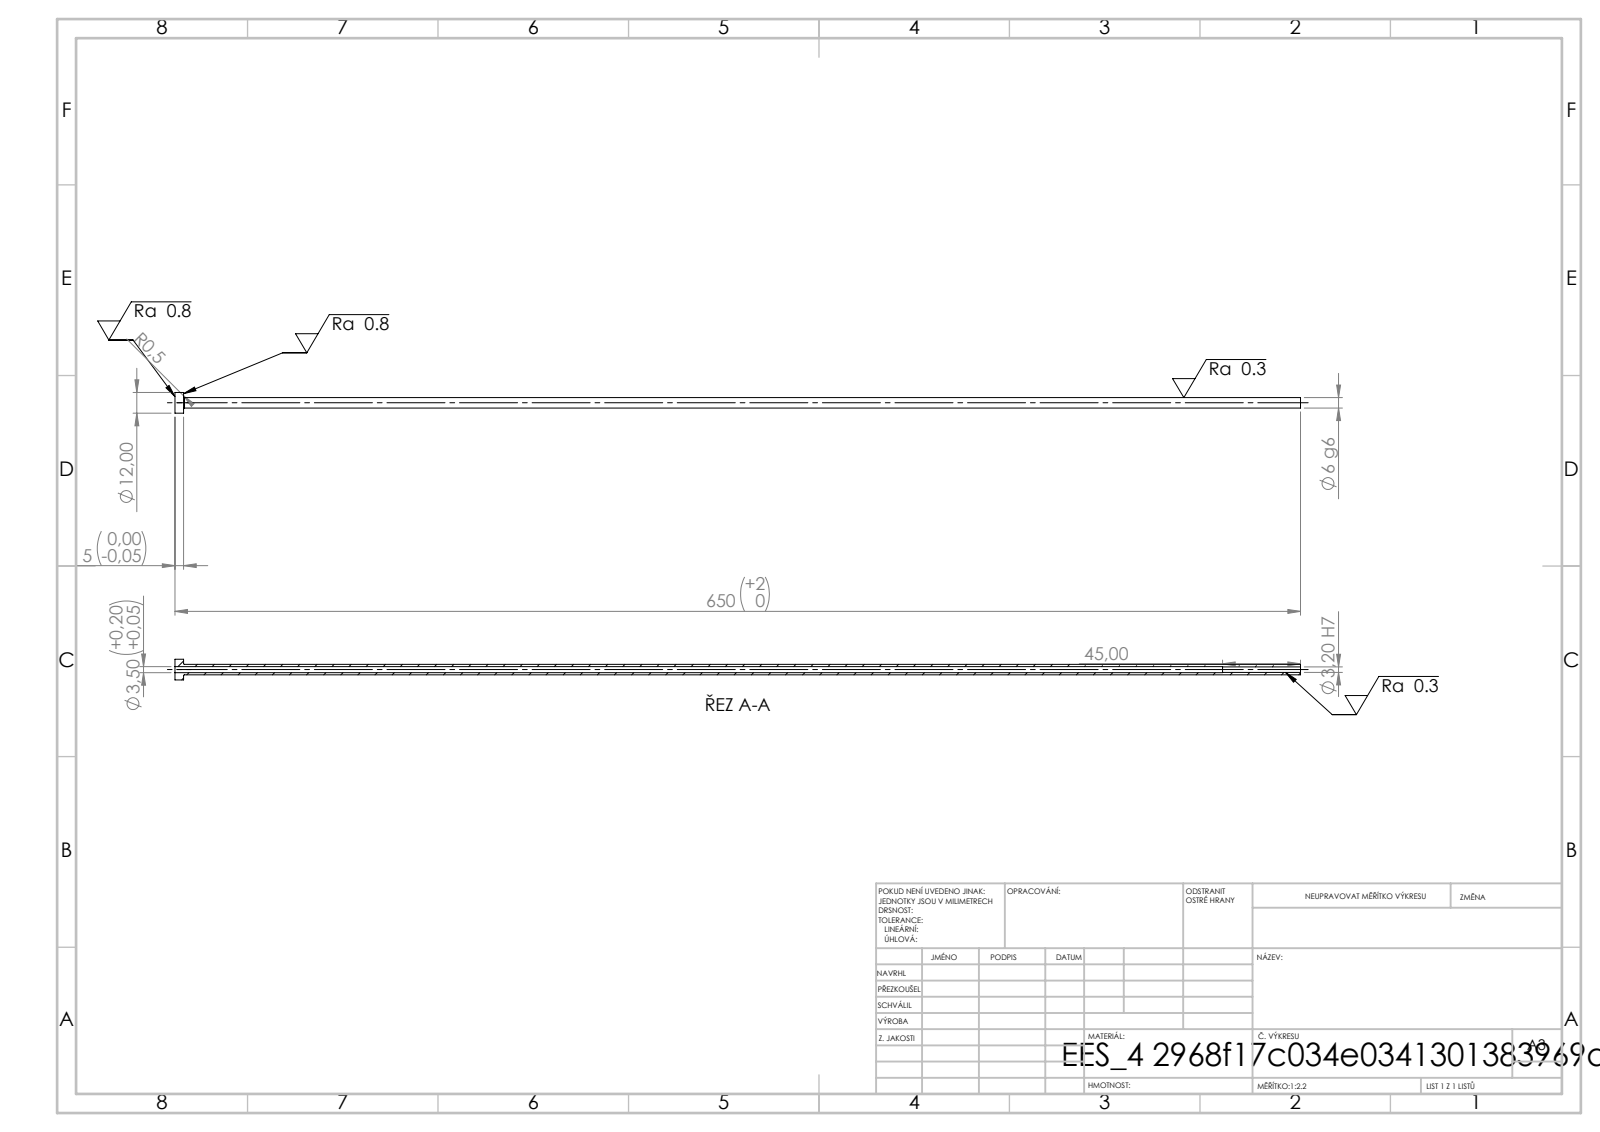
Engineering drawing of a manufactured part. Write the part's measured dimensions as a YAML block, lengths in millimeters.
step_written_by: "SolidWorks 2019 (CONFIG_CONTROL_DESIGN)"
units: millimeters
bodies: {solids: 1, faces: 14, planar: 4, cylindrical: 8, other: 2}
overall_size: [650, 12, 12]
volume: 12621
surface_area: 19657
round_holes:
  - {diameter: 3.2, count: 1}
  - {diameter: 3.5, count: 1}
round_bosses_or_shafts:
  - {diameter: 12, count: 1}
  - {diameter: 6, count: 1}
face_to_face_distances: [5, 650, 645, 605, 600, 45]
